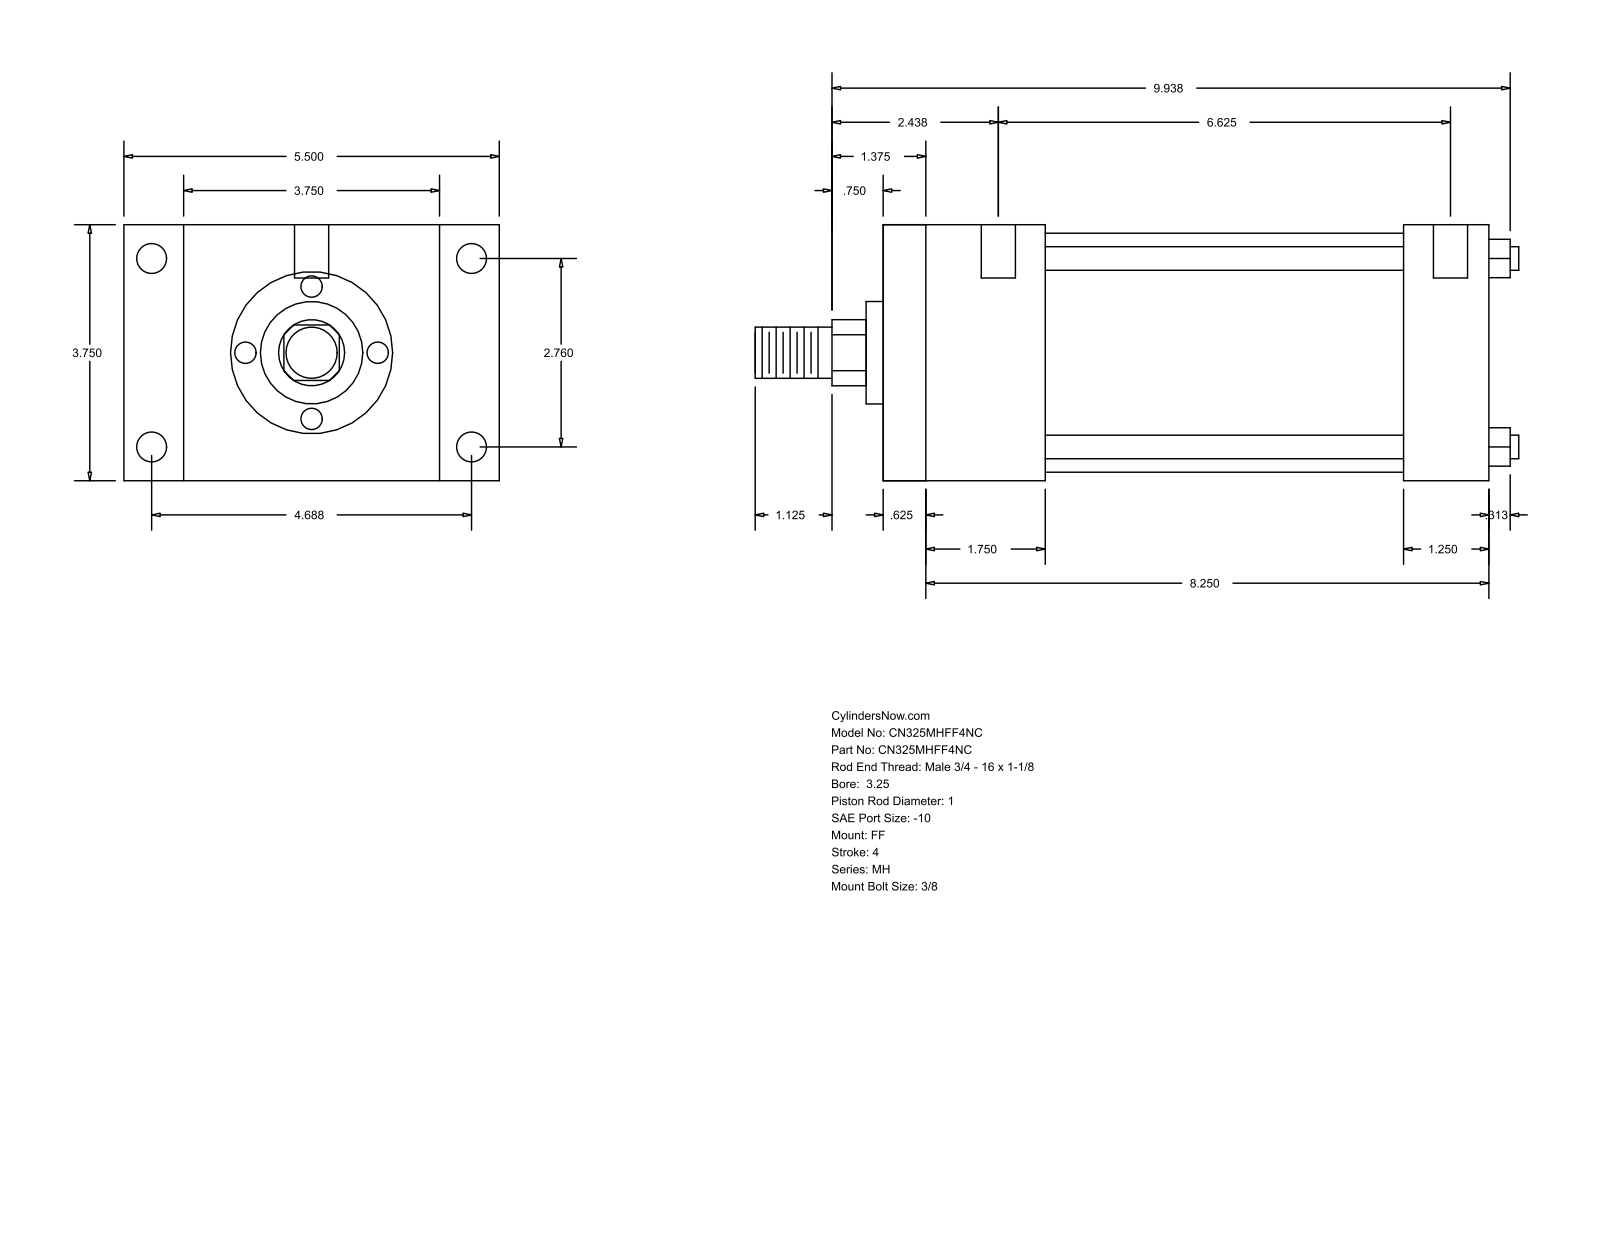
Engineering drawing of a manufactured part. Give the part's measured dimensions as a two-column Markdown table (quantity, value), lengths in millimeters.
| quantity | value |
| --- | --- |
| part name | MH_FF__0325_1 |
| STEP written by | GSSL Pune (CONFIG_CONTROL_DESIGN) |
| units | millimeters |
| bodies | 0 solids, 92 faces (64 planar, 28 cylindrical, 0 other) |
| overall size | 284.16 × 139.7 × 95.25 |
| round holes (diameter × count) | 5.56 × 4, 11.13 × 4, 12.7 × 2 |
| round bosses / shafts (diameter × count) | 8.76 × 4, 88.9 × 1, 38.1 × 1, 25.4 × 1, 19.05 × 1 |
| partial cylindrical surfaces (radius × count) | 12.29 × 1 |
| main face-to-face distances | 95.24, 225.42, 15.87, 209.55, 22.23, 117.47, 193.67, 177.8, 31.75, 60.33 |
| hole center spacings | 70.1, 119.06, 138.16, 174.62, 1.58, 4.76, 168.28, 169.86 |
